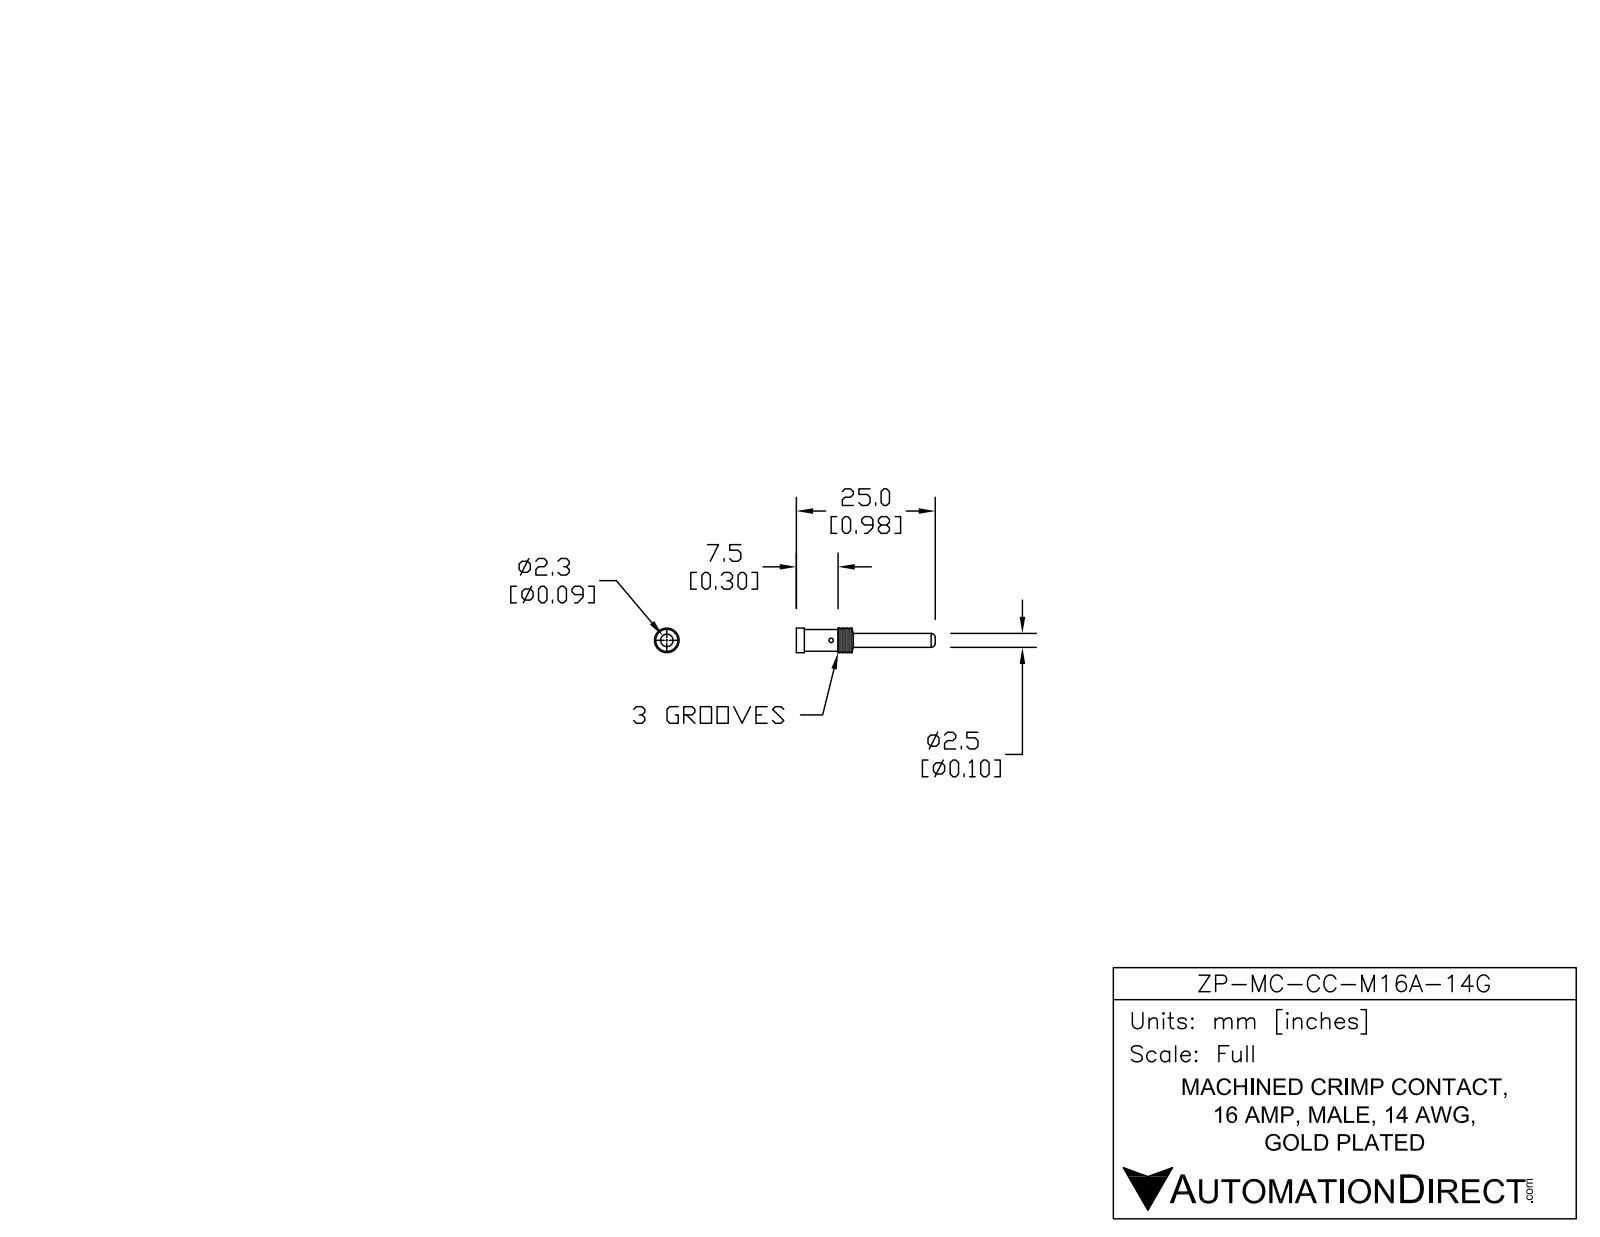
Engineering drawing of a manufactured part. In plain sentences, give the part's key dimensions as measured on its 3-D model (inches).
The part is named "ZP-MC-CC-M16A-14G". Its 3-D file was written by "SolidWorks 2014 (AUTOMOTIVE_DESIGN)". It is 1 solid with 42 faces: 10 planar, 24 cylindrical and 8 other. Overall it measures 0.984 by 0.174 by 0.174 inches. Its volume is 0.009 cubic inches and its surface area 0.524 square inches. Round holes: 1 of diameter 0.031, 1 of diameter 0.089. Round bosses or shafts: 1 of diameter 0.174, 1 of diameter 0.166, 1 of diameter 0.137, 1 of diameter 0.098. The main face-to-face distances are 0.014, 0.028, 0.295, 0.042, 0.02, 0.315, 0.07, 0.056, 0.014, 0.022.
